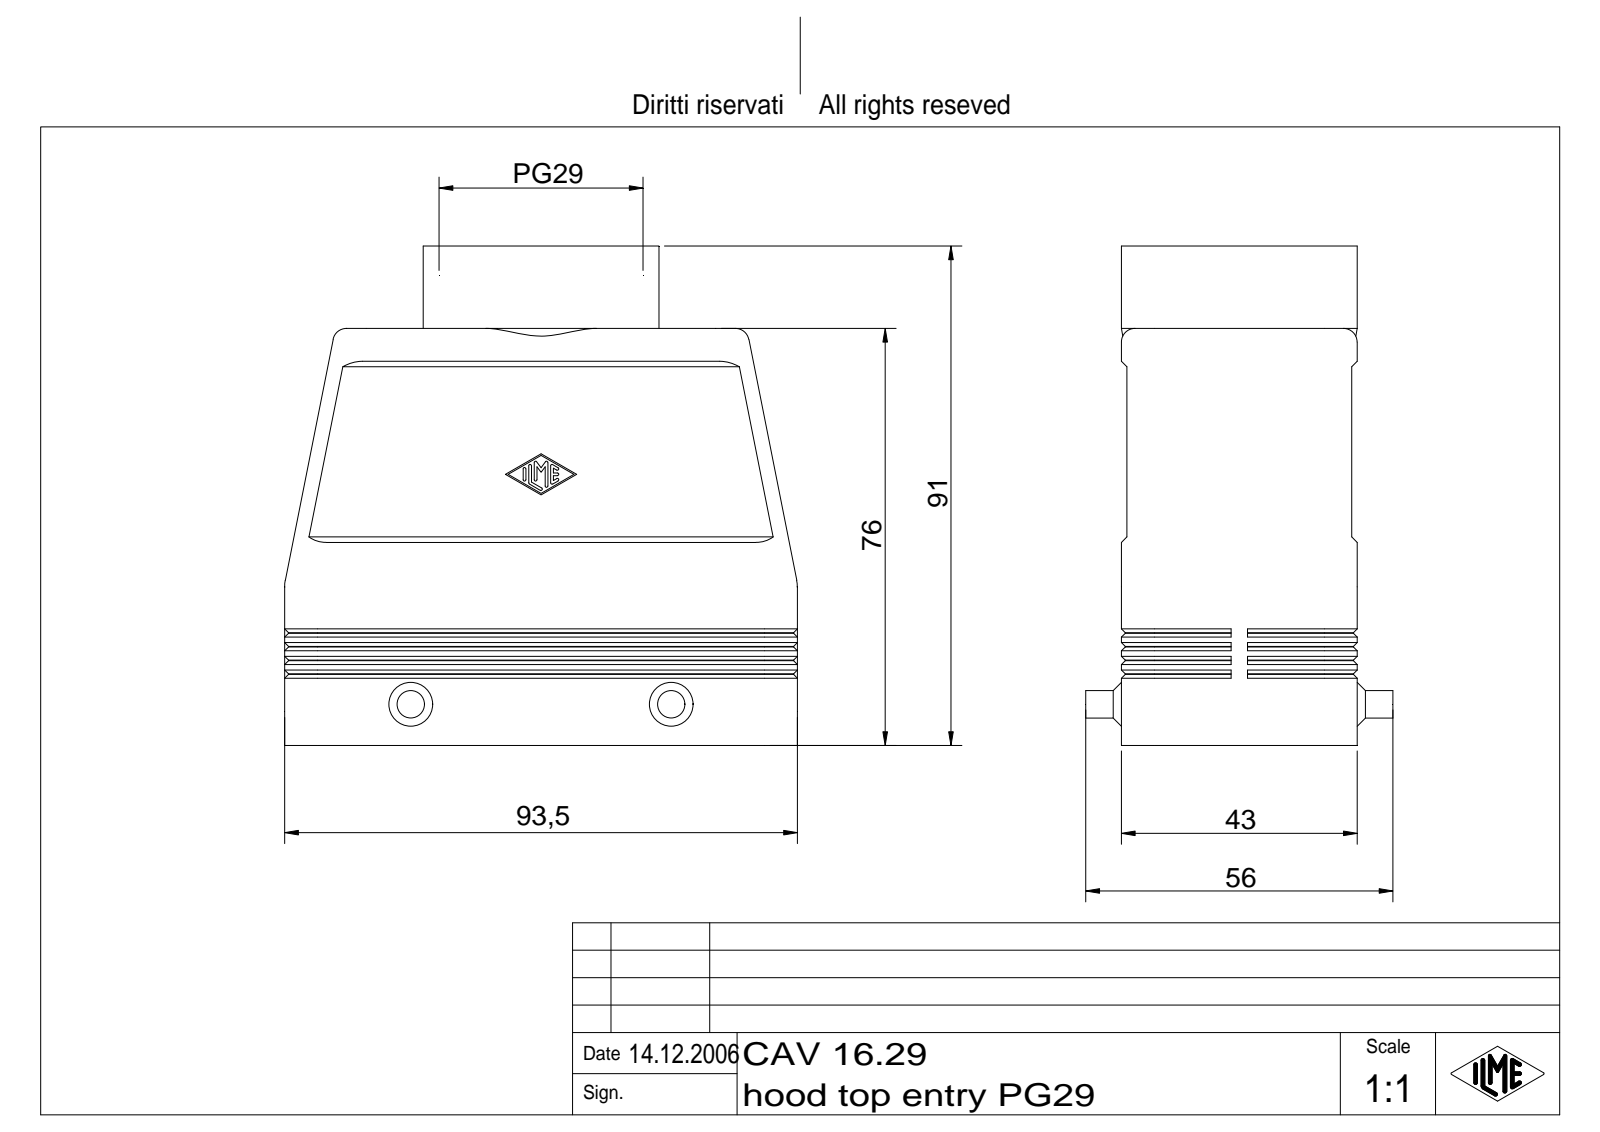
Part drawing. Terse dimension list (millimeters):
name: CAO Tüllengehäuse 2 Bügel für einen Einsatz
written by: Autodesk Inventor 7 (AUTOMOTIVE_DESIGN)
unit: mm
bodies: 1 solid, 413 faces (153 planar, 108 cylindrical, 152 other)
size: 93.5 × 91 × 56
volume: 77 342 mm³; area: 46 657 mm²
holes: 1× ⌀33.48, 1× ⌀35.48
bosses: 2× ⌀5, 1× ⌀43, 1× ⌀34.48
rounds: 14× R0.25, 10× R6, 4× R2, 4× R2.5, 4× R3, 2× R5.3
face distances: 3, 40, 37, 1, 2, 42, 39, 43, 41, 12.25
